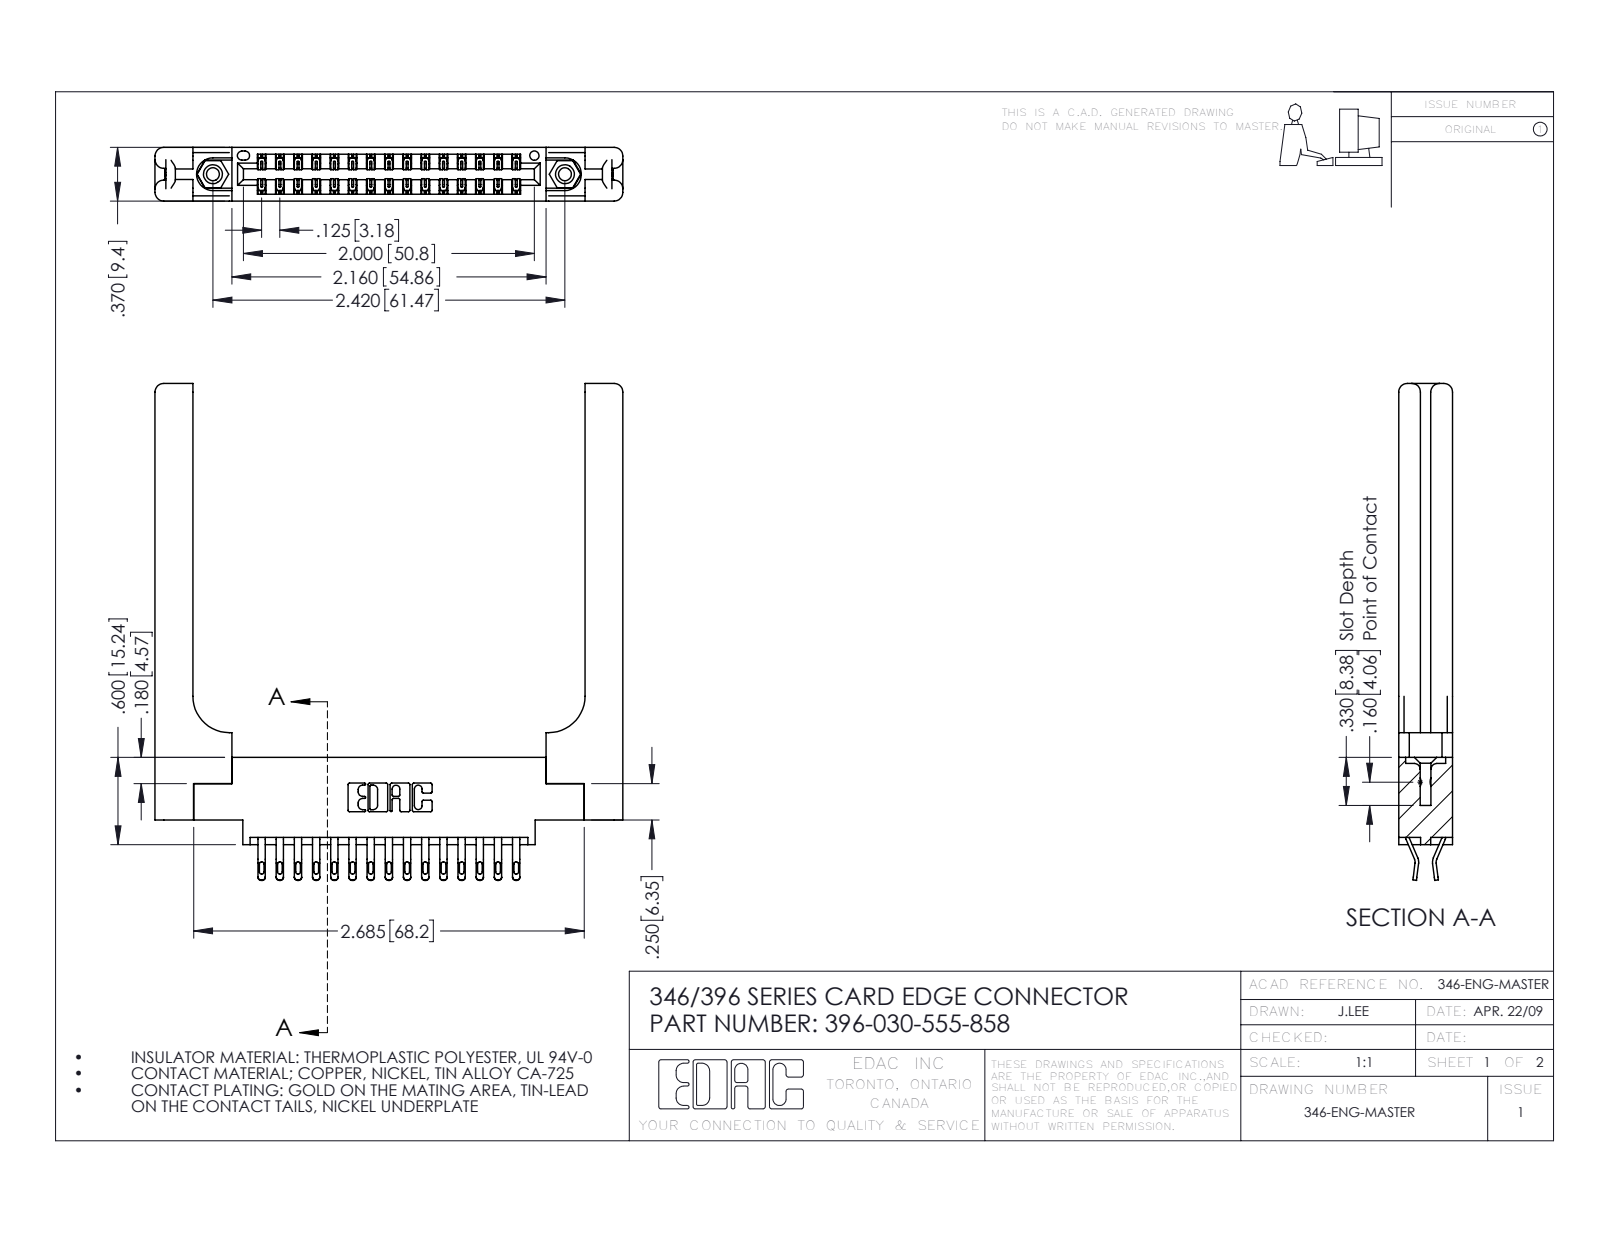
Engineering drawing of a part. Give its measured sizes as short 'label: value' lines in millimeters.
name: 396-030-555-858; 346 Part_0.170 Offset - 0.156 Dia-TH; 345-292-001_555 Tail; 346-220-058_345-220-058 (+1 more)
written by: SolidWorks 2016 (CONFIG_CONTROL_DESIGN)
unit: mm
bodies: 35 solids, 2122 faces (1218 planar, 844 cylindrical, 60 other)
size: 86.7 × 81.7 × 9.4
volume: 15 200 mm³; area: 15 610 mm²
holes: 2× ⌀2.3, 2× ⌀3.2, 2× ⌀4, 1× ⌀1.6
bosses: 2× ⌀3.9
rounds: 60× R0.4, 60× R0.5, 45× R0.2, 22× R0.3, 16× R1.5, 6× R0.2, 6× R0.8, 3× R0.7
face distances: 9.4, 3.8, 1.8, 3.8, 1.2, 8.2, 6.4, 2.6, 5.6, 4.4
hole spacings: 6.2, 56.2, 61.5
